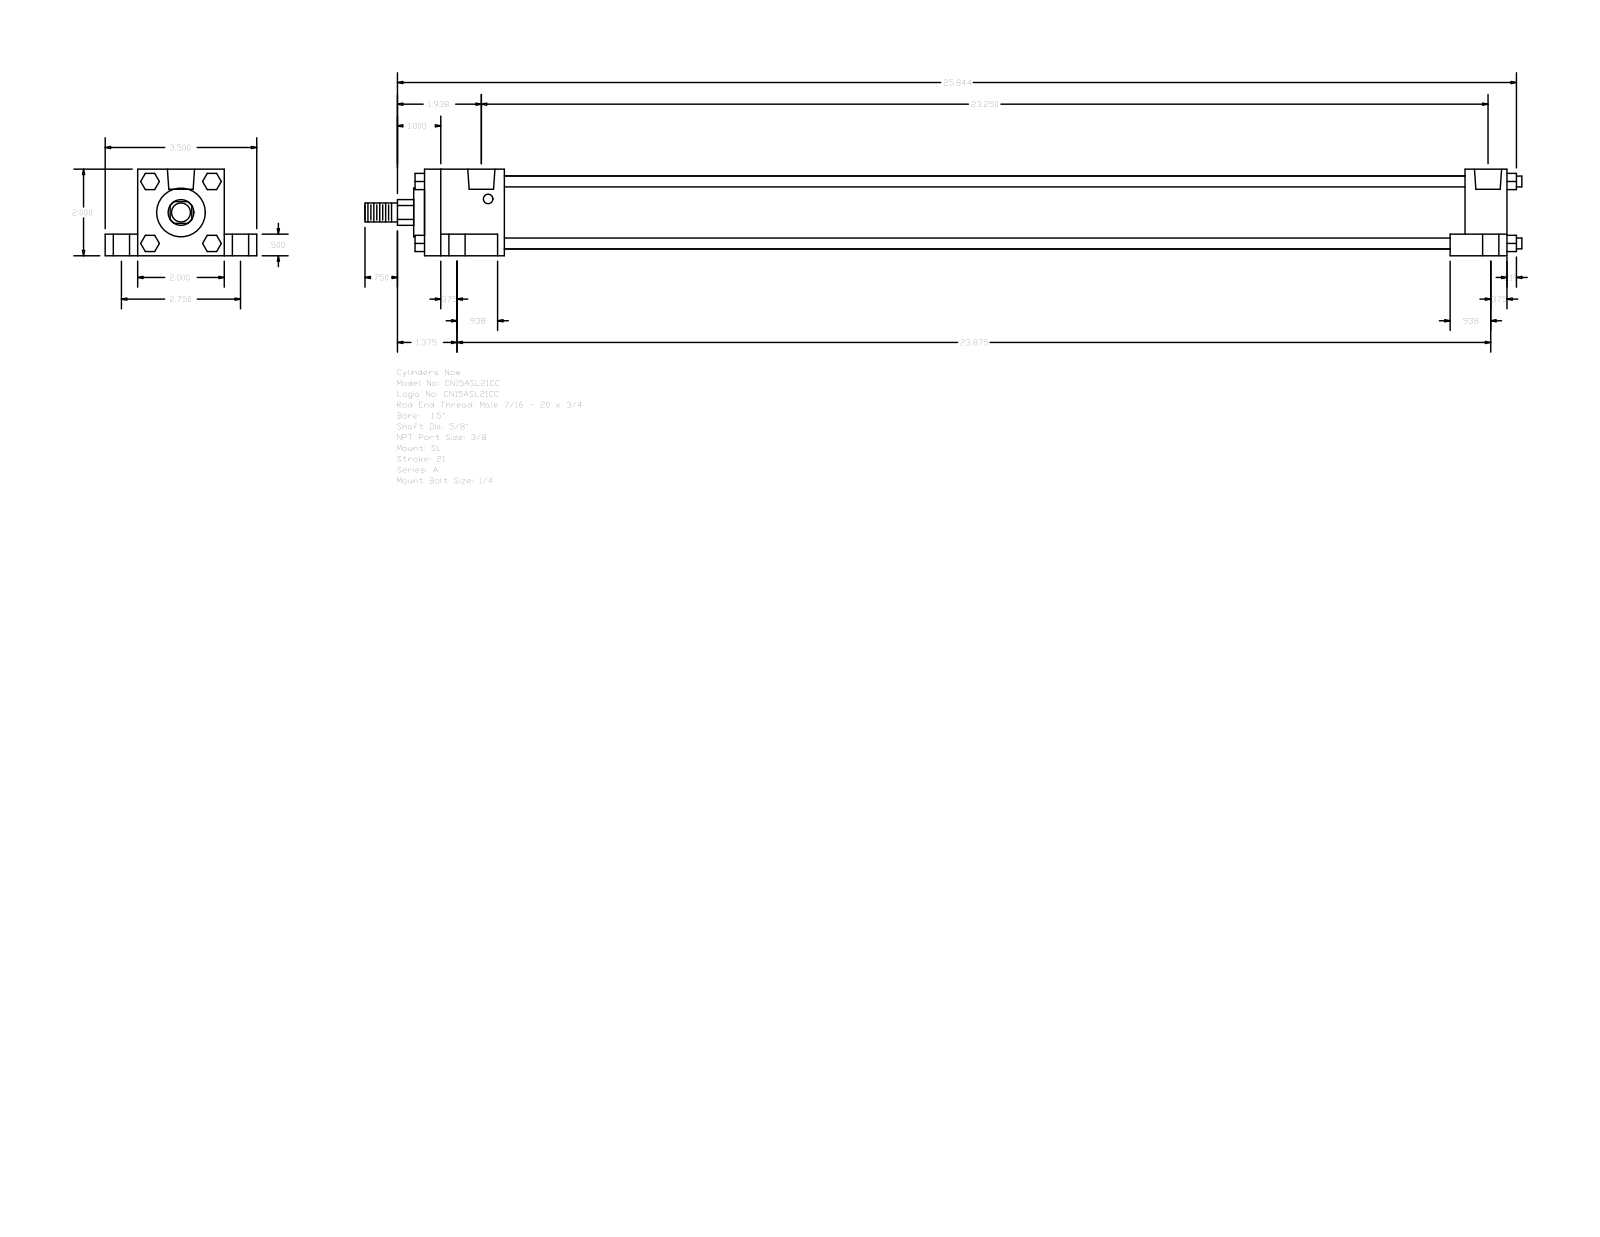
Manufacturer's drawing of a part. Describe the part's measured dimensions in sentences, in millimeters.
The part is named "A_SL__0150_0.625". Its 3-D file was written by "GSSL Pune (CONFIG_CONTROL_DESIGN)". It is 0 solids with 148 faces: 112 planar, 36 cylindrical and 0 other. Overall it measures 678.66 by 88.9 by 50.8 millimeters. Round holes: 4 of diameter 5.56, 4 of diameter 9.53, 4 of diameter 15.88, 2 of diameter 15.93. Round bosses or shafts: 4 of diameter 6.35, 1 of diameter 42.93, 1 of diameter 28.57, 1 of diameter 15.88, 1 of diameter 11.11. Partial cylindrical surfaces (rounded edges, fillets, slot ends): 1 of radius 7.54. The main face-to-face distances are 50.8, 19.05, 38.1, 12.7, 69.85, 635, 9.52, 33.34, 610.39, 24.61. The hole center spacings are 3.97, 34.96, 35.36, 37.73, 39.41, 69.84, 582.61, 586.58.
